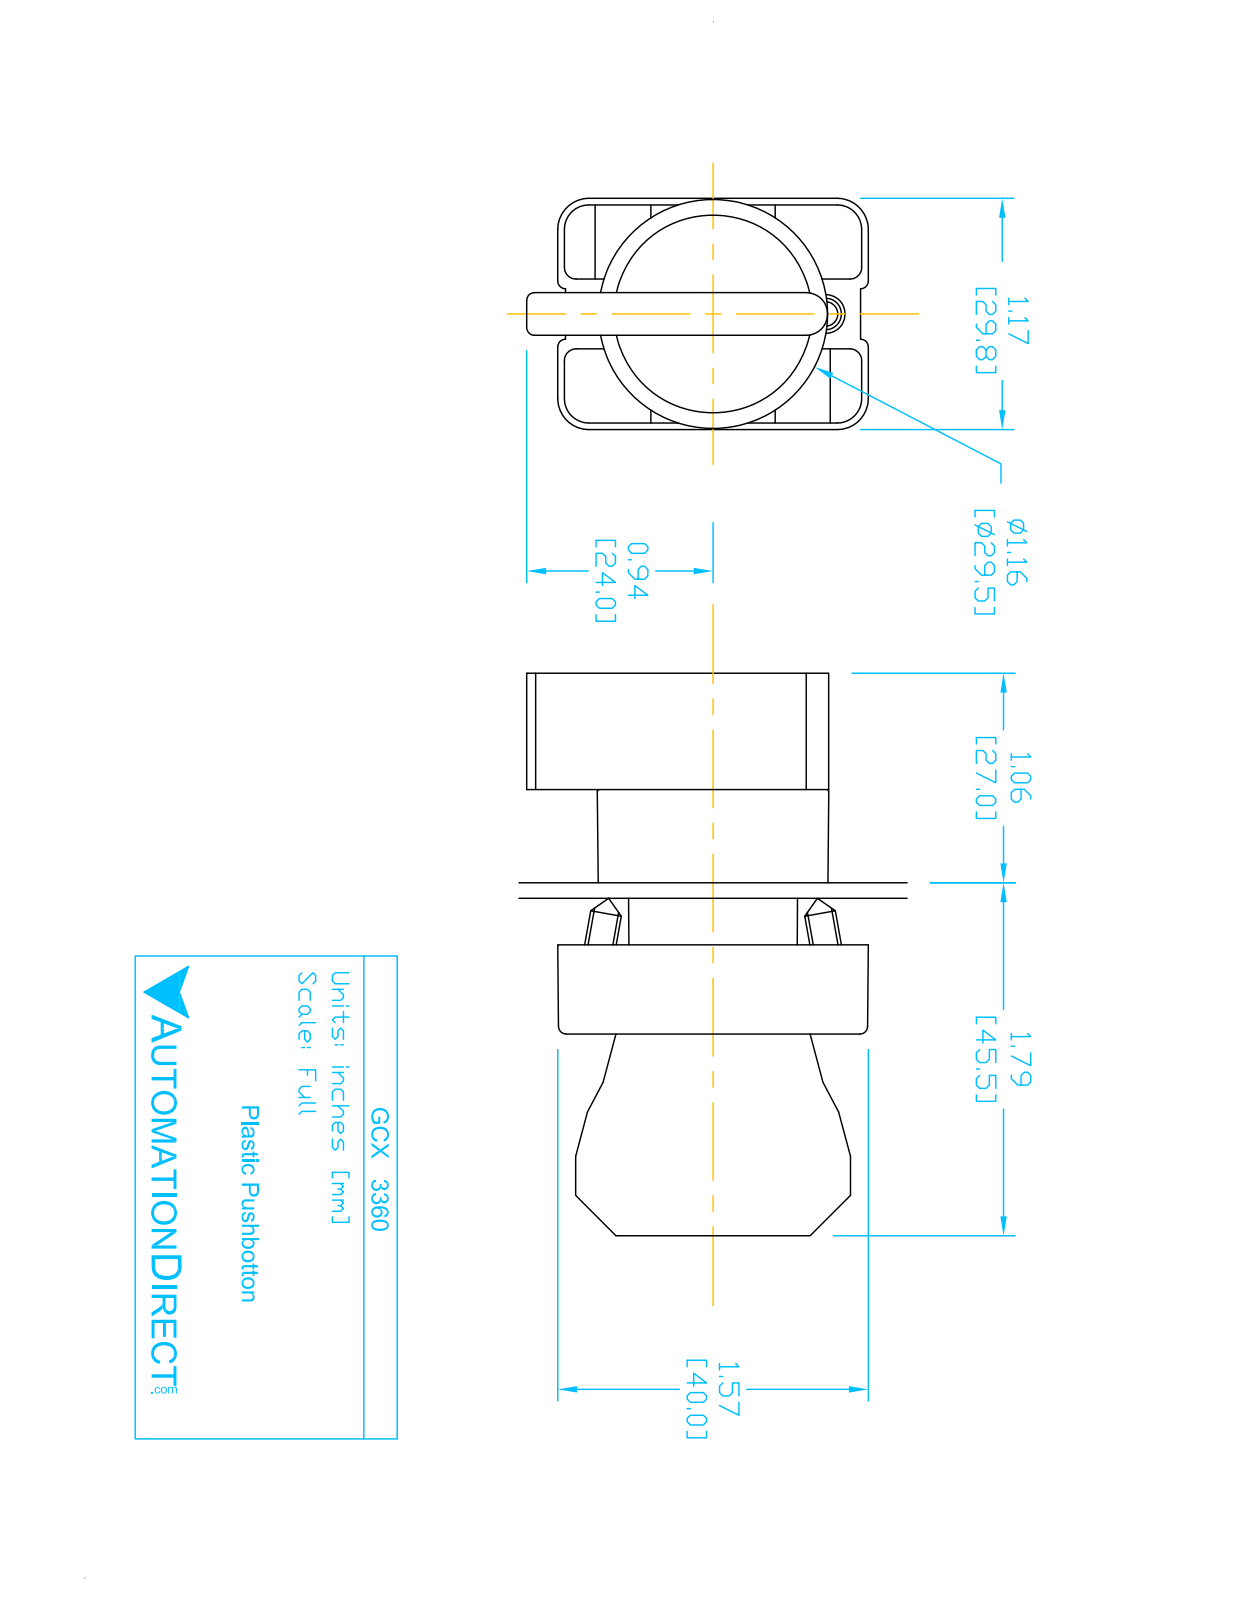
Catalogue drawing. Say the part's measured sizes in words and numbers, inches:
The part is named "GCX3360; ecx1040; GCX3360 OPERATOR; ECX3029-2". Its 3-D file was written by "SolidWorks 2016 (AUTOMOTIVE_DESIGN)". It is 6 solids with 396 faces: 232 planar, 137 cylindrical and 27 other. Overall it measures 2.78 by 1.752 by 1.177 inches. Its volume is 1.929 cubic inches and its surface area 29.25 square inches. Round holes: 2 of diameter 0.079, 2 of diameter 0.124, 2 of diameter 0.13, 1 of diameter 0.087, 1 of diameter 0.197, 1 of diameter 0.878, 1 of diameter 0.888, 1 of diameter 1.024. Round bosses or shafts: 2 of diameter 0.157, 1 of diameter 1.175, 1 of diameter 1.004, 1 of diameter 0.945, 1 of diameter 0.856, 1 of diameter 0.78. Partial cylindrical surfaces (rounded edges, fillets, slot ends): 24 of radius 0.059, 12 of radius 0.041, 12 of radius 0.124, 12 of radius 0.157, 6 of radius 0.039, 2 of radius 0.128, 1 of radius 0.02, 1 of radius 0.063. The main face-to-face distances are 0.72, 0.579, 0.472, 0.033, 0.474, 0.703, 0.031, 0.124, 1.193, 1.024. The hole center spacings are 0.236, 0.544, 0.472, 0.49.
